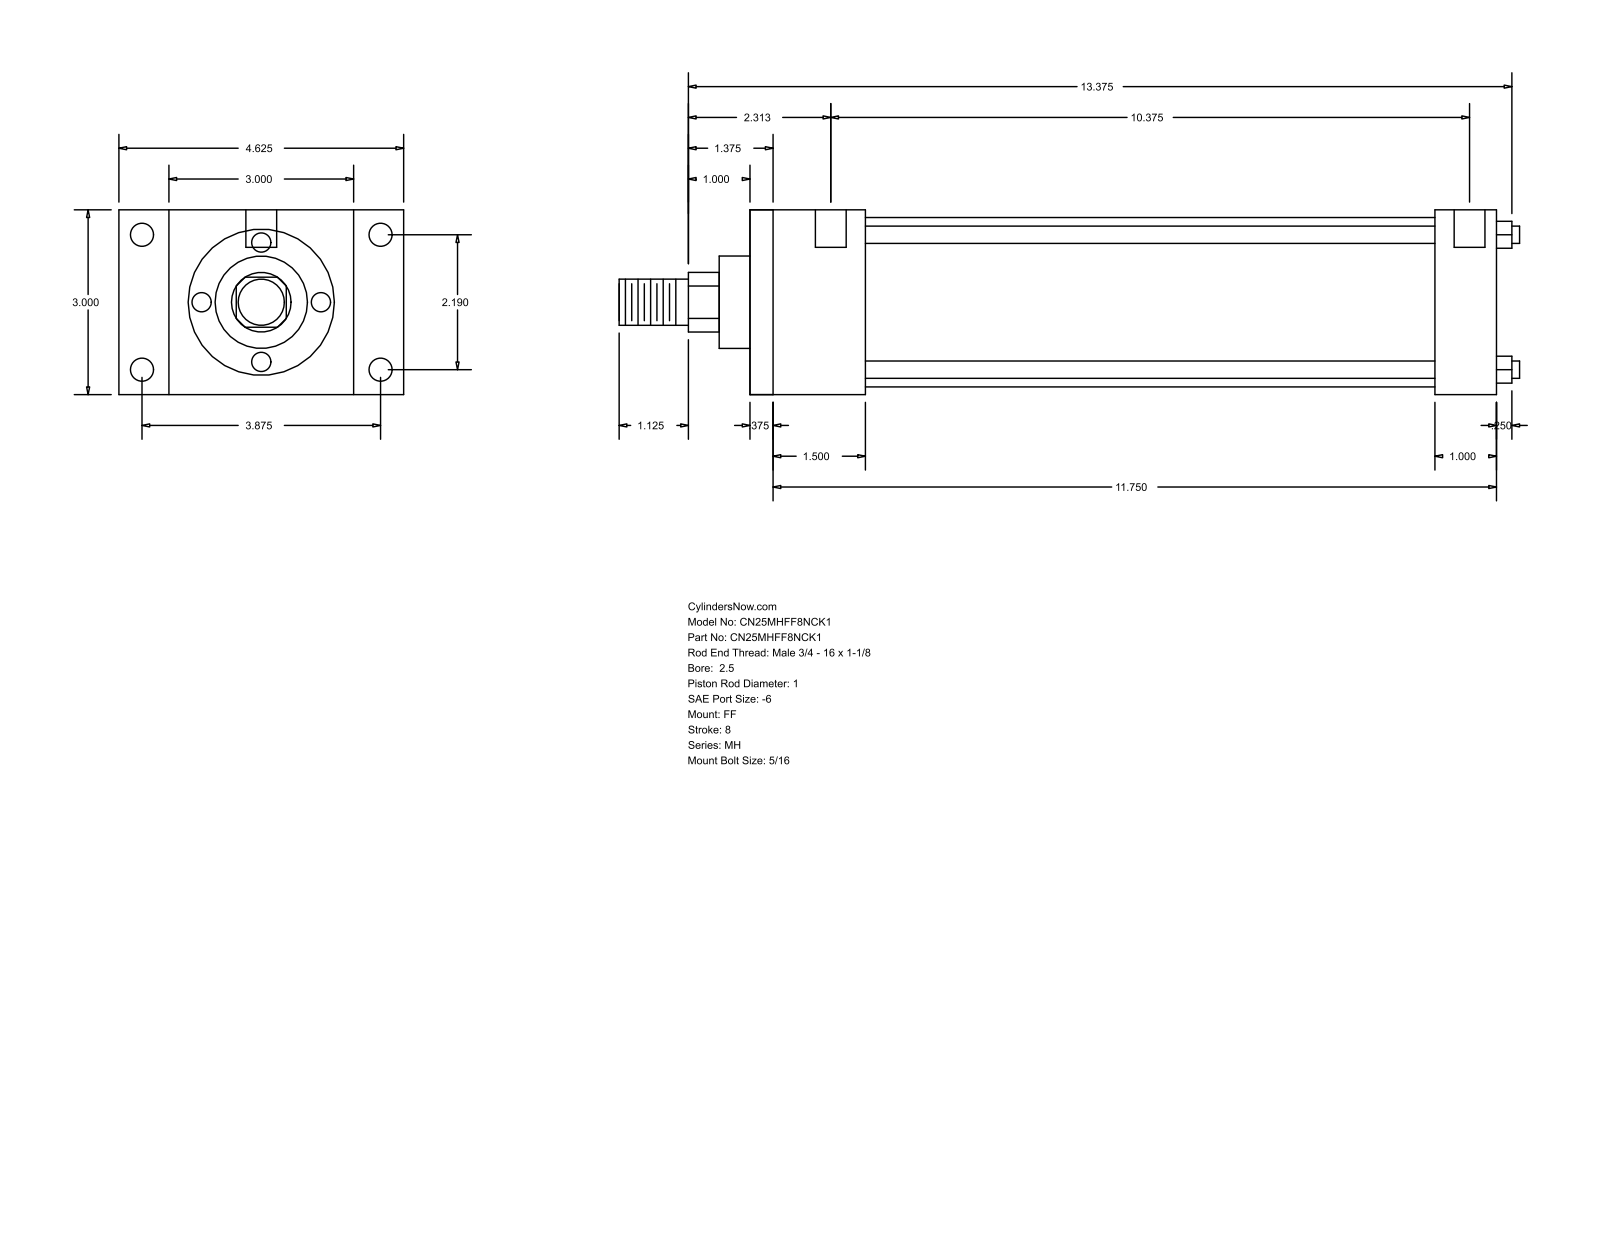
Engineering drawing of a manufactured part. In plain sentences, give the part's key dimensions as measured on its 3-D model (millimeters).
The part is named "MH_FF__0250_1". Its 3-D file was written by "GSSL Pune (CONFIG_CONTROL_DESIGN)". It is 0 solids with 92 faces: 64 planar, 28 cylindrical and 0 other. Overall it measures 371.48 by 117.47 by 76.2 millimeters. Round holes: 4 of diameter 5.56, 4 of diameter 9.53, 2 of diameter 12.7. Round bosses or shafts: 4 of diameter 7.14, 1 of diameter 69.85, 1 of diameter 38.1, 1 of diameter 25.4, 1 of diameter 19.05. Partial cylindrical surfaces (rounded edges, fillets, slot ends): 1 of radius 12.29. The main face-to-face distances are 76.2, 307.98, 9.52, 298.46, 25.4, 47.63, 282.58, 38.11, 273.06, 234.95. The hole center spacings are 55.62, 98.42, 113.05, 271.46, 3.18, 4.76, 263.52, 266.7.
